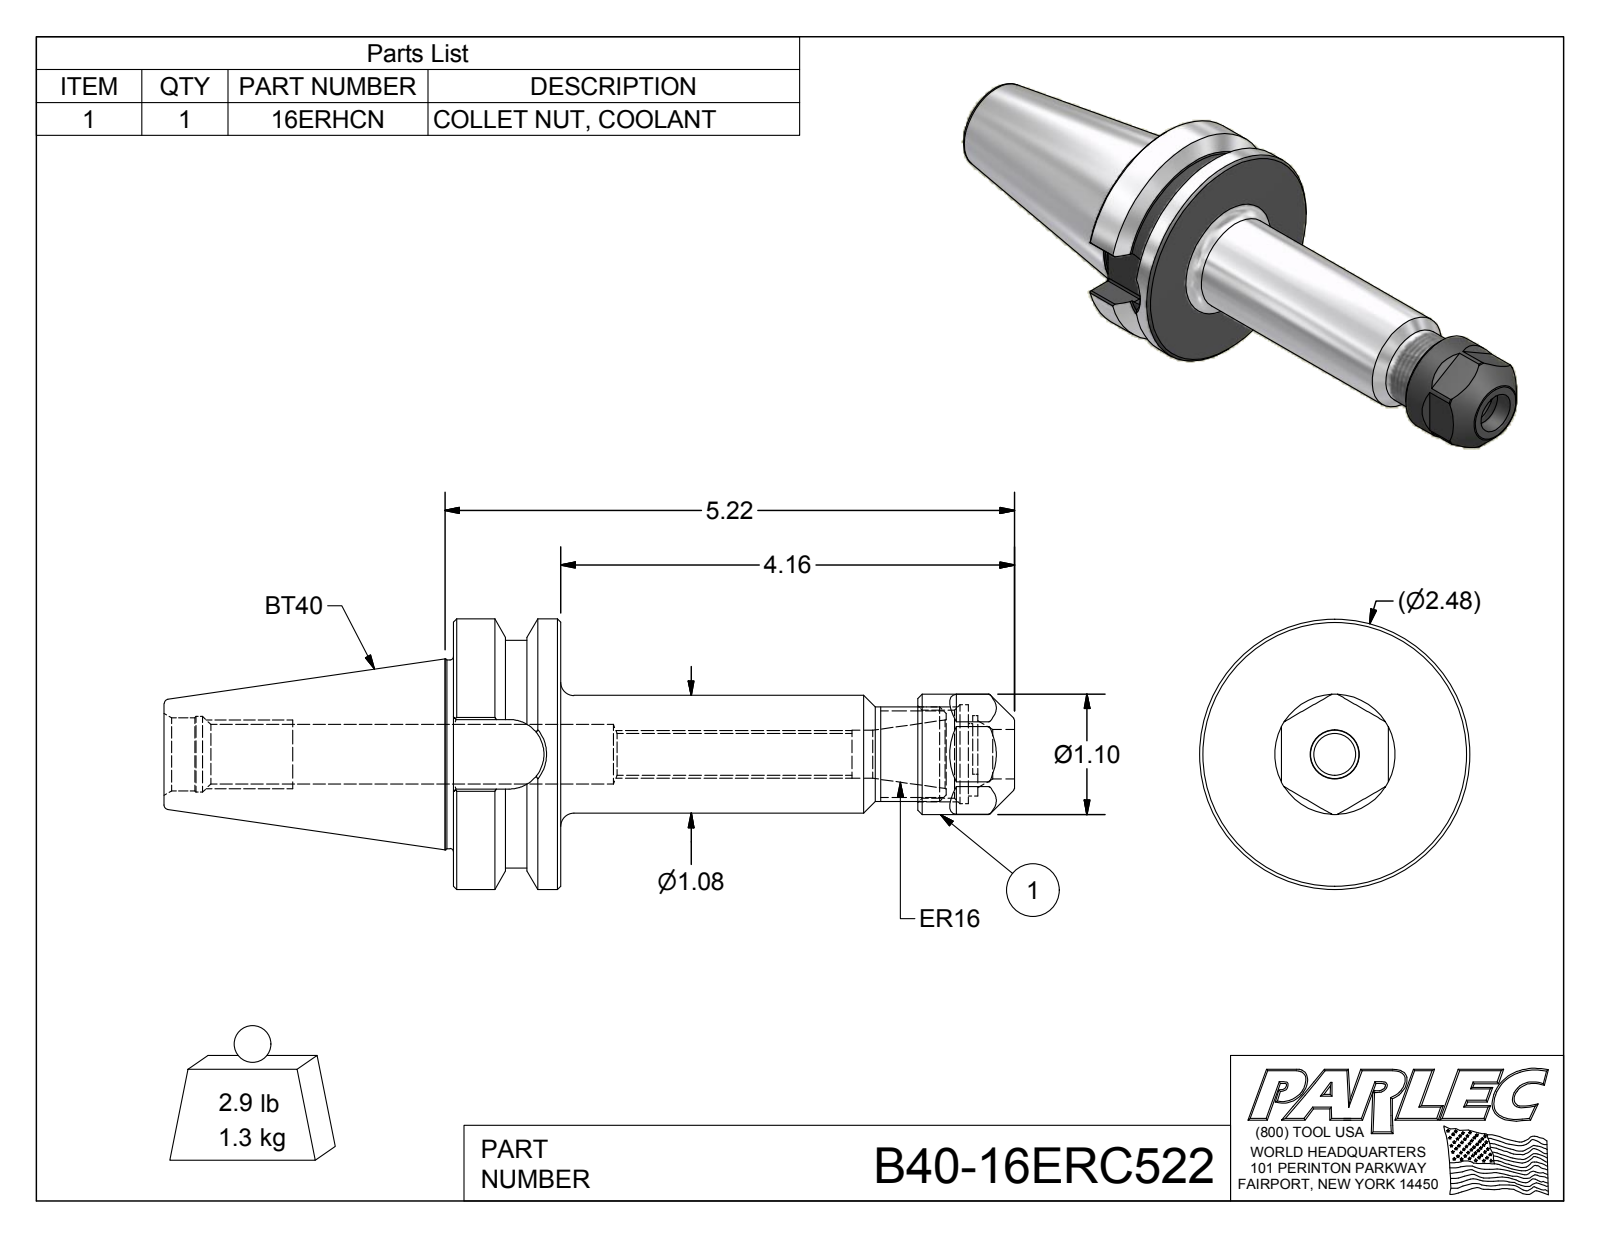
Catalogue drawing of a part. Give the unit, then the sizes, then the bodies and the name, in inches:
Units: inches
Overall size (bounding box): 7.795 × 2.48 × 2.48
Round holes (diameter × count): ⌀0.383 ×1, ⌀0.44 ×1, ⌀0.453 ×1, ⌀0.545 ×1, ⌀0.661 ×1, ⌀0.67 ×1, ⌀0.694 ×1, ⌀0.807 ×1, ⌀0.906 ×1
Round bosses / shafts (diameter × count): ⌀2.48 ×1, ⌀2.087 ×1, ⌀1.73 ×1, ⌀1.102 ×1, ⌀1.08 ×1, ⌀0.866 ×1
Partial cylindrical surfaces — rounded edges, fillets, slot ends (radius × count): R0.02 ×8, R0.319 ×1, R0.354 ×1
Main face-to-face distances: 0.984, 0.979, 1.78, 0.401, 1.38, 4.721, 3.737, 2.653, 3.637, 7.374
Hole centre spacings: 0.051
Volume: 10.12 in³ · Surface area: 56.58 in²
Bodies: 2 solids, 106 faces (41 planar, 29 cylindrical, 36 other)
Part name (STEP PRODUCT): B40-16ERC522; B40-16ER5-1; 16ERHCN
STEP written by: Autodesk Inventor 2012 (AUTOMOTIVE_DESIGN)
